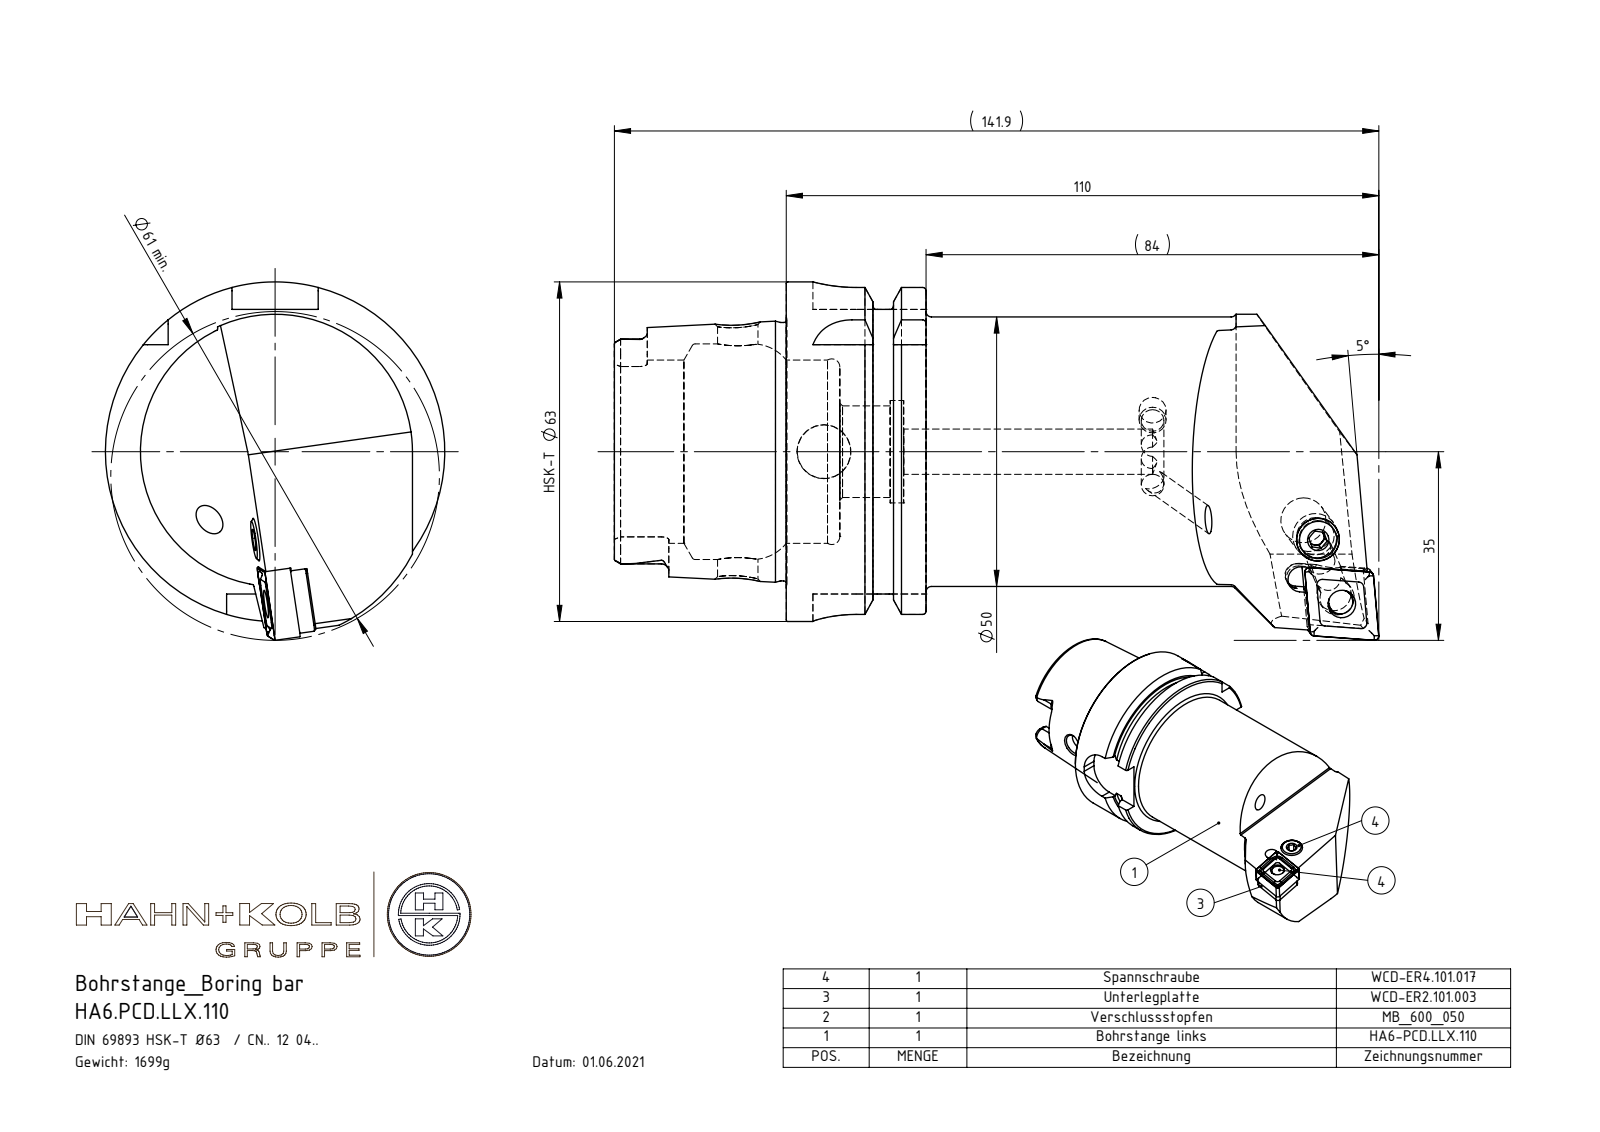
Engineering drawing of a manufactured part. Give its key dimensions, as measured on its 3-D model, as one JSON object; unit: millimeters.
{"part_name": "WCD-ER4.101.017_A; HA6-PCD.LLX.110_A; KVT_MB_600_050; CNMG120408 (+4 more)", "step_written_by": "SolidWorks 2017 (AUTOMOTIVE_DESIGN)", "units": "millimeters", "bodies": {"solids": 7, "faces": 281, "planar": 116, "cylindrical": 67, "other": 98}, "overall_size": [141.9, 66.5, 63], "volume_mm3": 215702, "surface_area_mm2": 39032, "round_holes": [[4.2, 2], [8.4, 2], [4, 1], [5, 1], [5.16, 1], [6.4, 1], [7, 1], [7.5, 1], [10, 1], [17, 1], [19, 1], [34, 1]], "round_bosses_or_shafts": [[63, 1], [54.95, 1], [50, 1], [47.94, 1], [8, 1], [7.9, 1], [6.4, 1], [5, 1]], "partial_cylinders_radius": [[1.4, 6], [0.8, 4], [1, 4], [8, 4], [2.5, 2], [2.82, 2], [2.88, 2], [0.5, 1]], "face_to_face_distances": [25.95, 16, 9.95, 31.9, 41.85, 57.85, 52.8, 21.8, 11.85, 4.5], "hole_center_spacings": [12.82, 12.87]}
